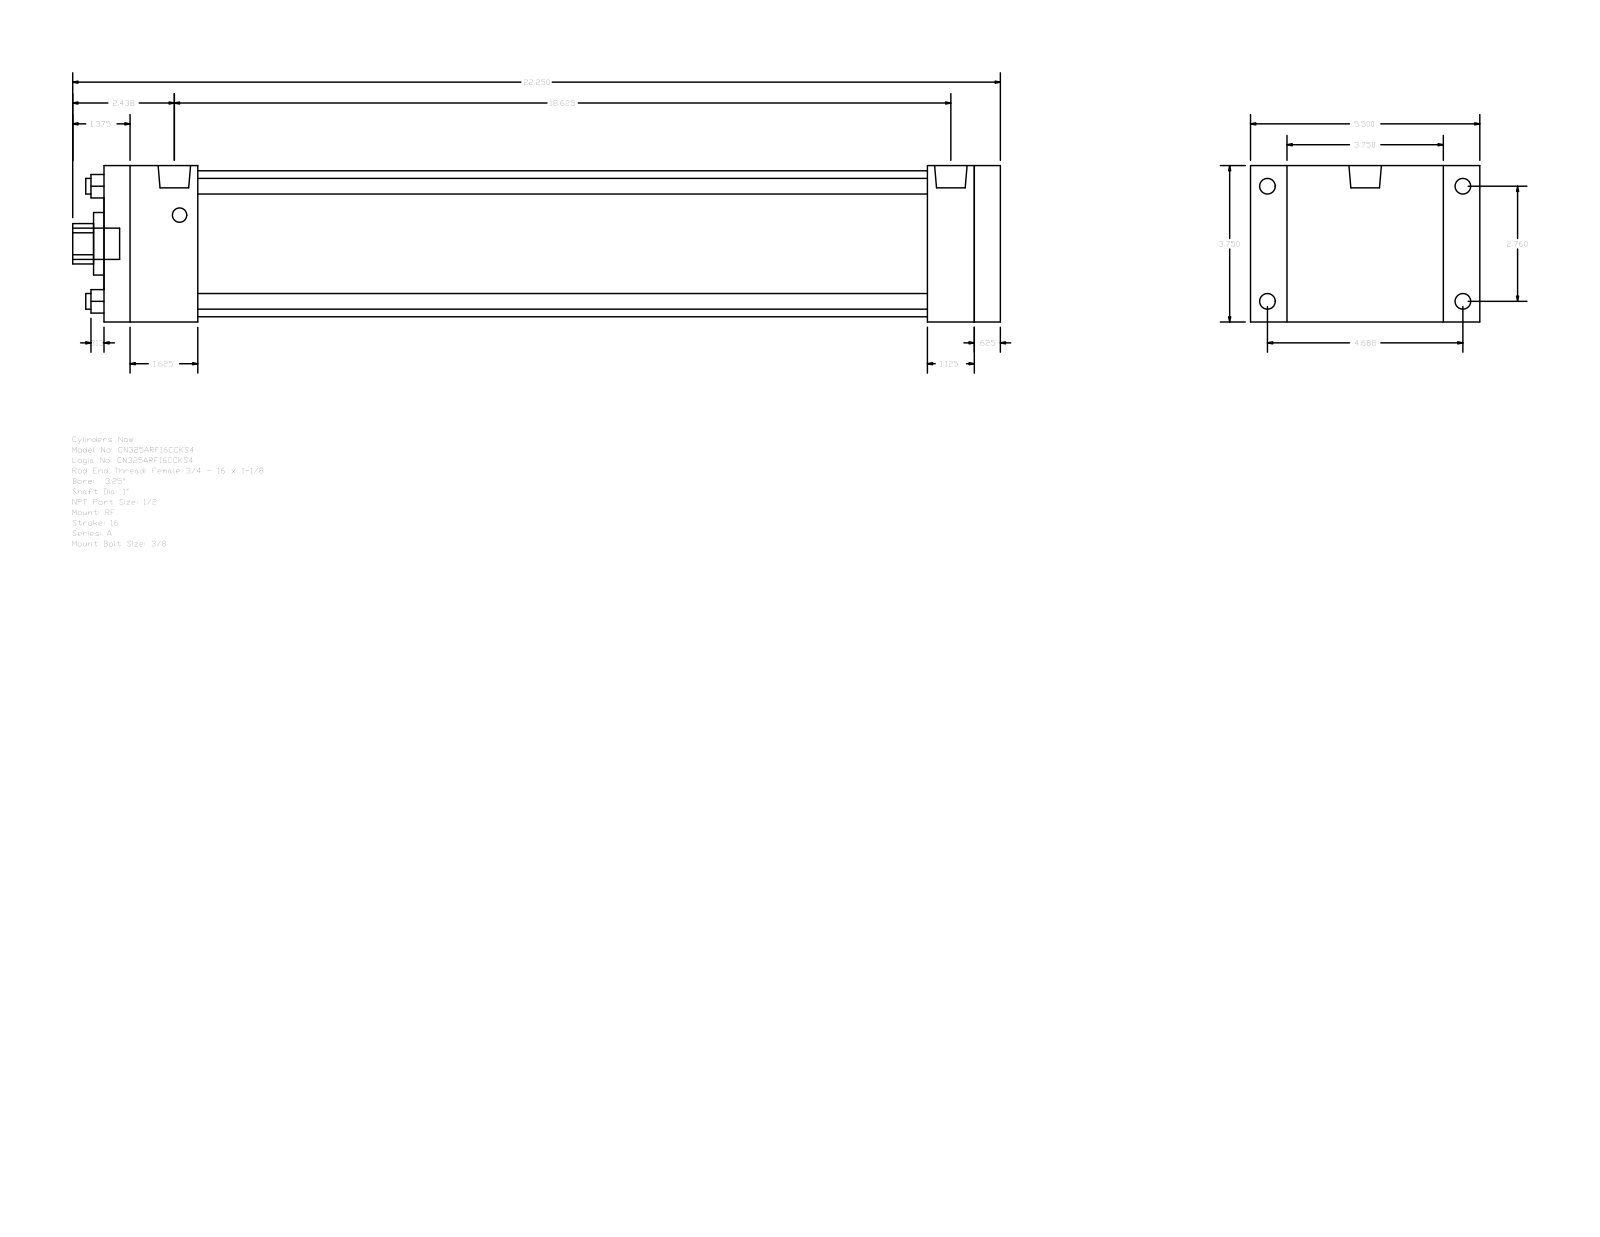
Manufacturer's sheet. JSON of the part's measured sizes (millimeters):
{"part_name": "A_RF__0325_1", "step_written_by": "GSSL Pune (CONFIG_CONTROL_DESIGN)", "units": "millimeters", "bodies": {"solids": 0, "faces": 92, "planar": 64, "cylindrical": 28, "other": 0}, "overall_size": [565.15, 139.7, 95.25], "round_holes": [[9.53, 4], [25.4, 1], [38.1, 1], [88.9, 1]], "round_bosses_or_shafts": [[9.53, 4], [8.73, 4], [19.77, 2], [19.05, 1]], "partial_cylinders_radius": [[12.29, 1]], "face_to_face_distances": [95.24, 546.1, 530.22, 15.88, 22.23, 117.47, 28.57, 501.65, 44.45, 57.15], "hole_center_spacings": [49.57, 70.1, 99.14]}
